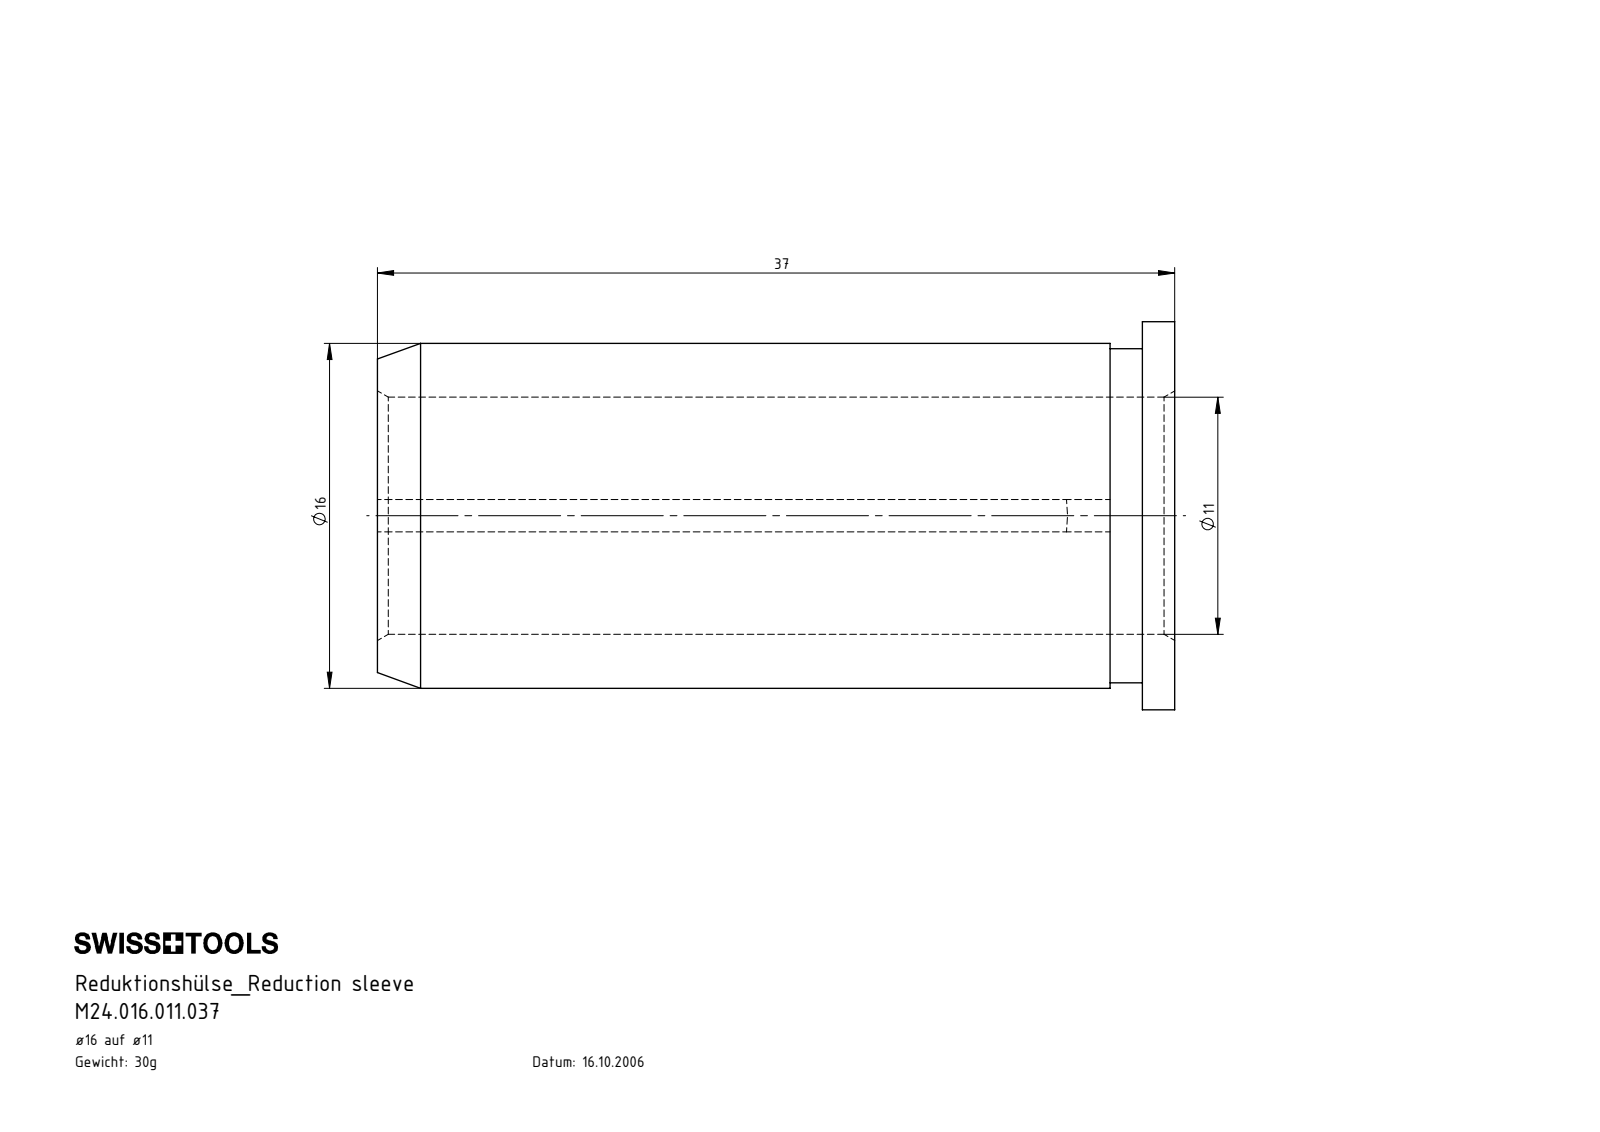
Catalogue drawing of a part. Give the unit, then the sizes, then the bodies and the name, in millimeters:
Units: millimetres
Overall size (bounding box): 37 × 18 × 18
Round holes (diameter × count): ⌀11 ×1
Round bosses / shafts (diameter × count): ⌀18 ×1, ⌀16 ×1, ⌀15.5 ×1
Partial cylindrical surfaces — rounded edges, fillets, slot ends (radius × count): R31.5 ×1
Main face-to-face distances: 1.5, 35.5, 37, 34, 3
Volume: 3 821 mm³ · Surface area: 3 509 mm²
Bodies: 1 solid, 14 faces (6 planar, 5 cylindrical, 3 other)
Part name (STEP PRODUCT): U11.U16.001.037
STEP written by: SolidWorks 2017 (AUTOMOTIVE_DESIGN)
